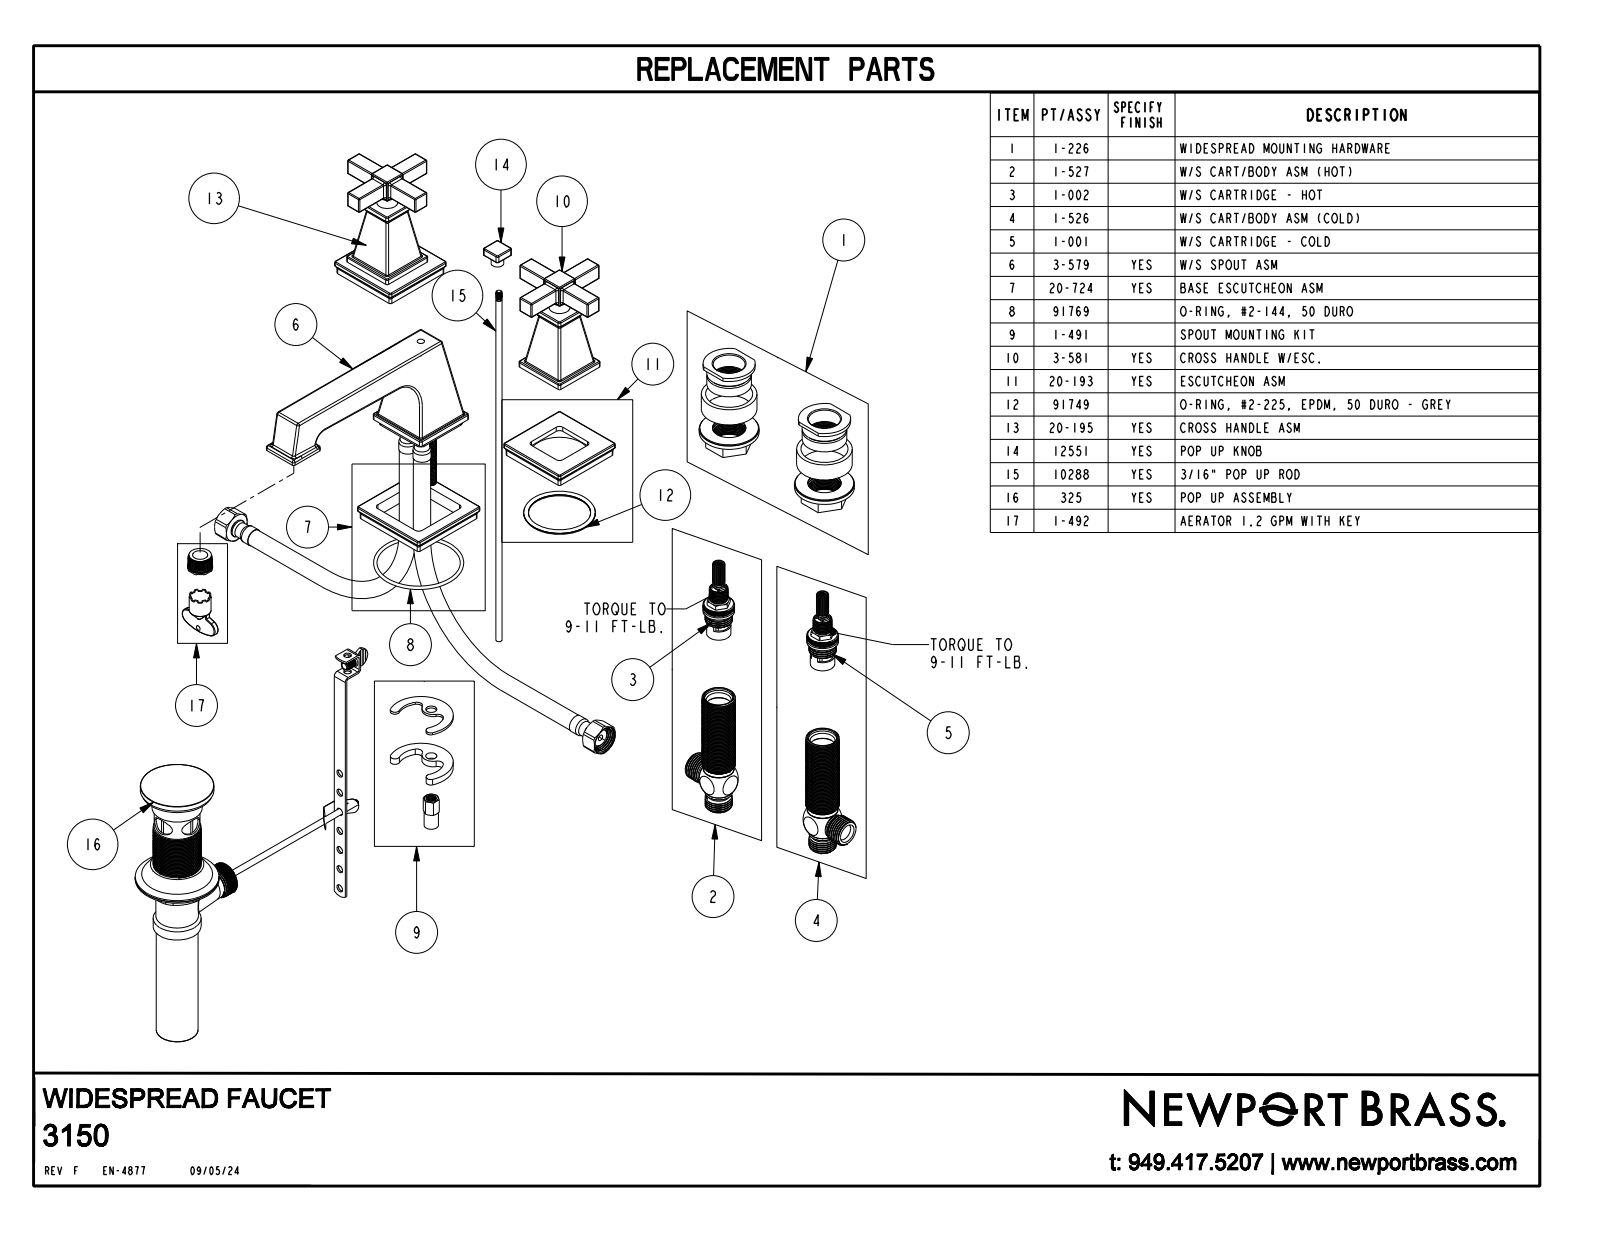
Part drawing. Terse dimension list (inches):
name: 3150
written by: CREO PARAMETRIC BY PTC INC, 2018400 (CONFIG_CONTROL_DESIGN)
unit: in
bodies: 3 solids, 788 faces (154 planar, 330 cylindrical, 304 other)
size: 10.875 × 7.406 × 3.8
volume: 27.76 in³; area: 126.4 in²
bosses: 2× ⌀0.625, 2× ⌀0.506, 1× ⌀0.375
rounds: 120× R0.03, 113× R0.06, 16× R0.09, 8× R0.23, 2× R1, 1× R0.375, 1× R0.75
face distances: 0.41, 0.5, 3.25, 2.84, 2.5, 3.76, 7.88, 4.12, 3.035, 3.535
